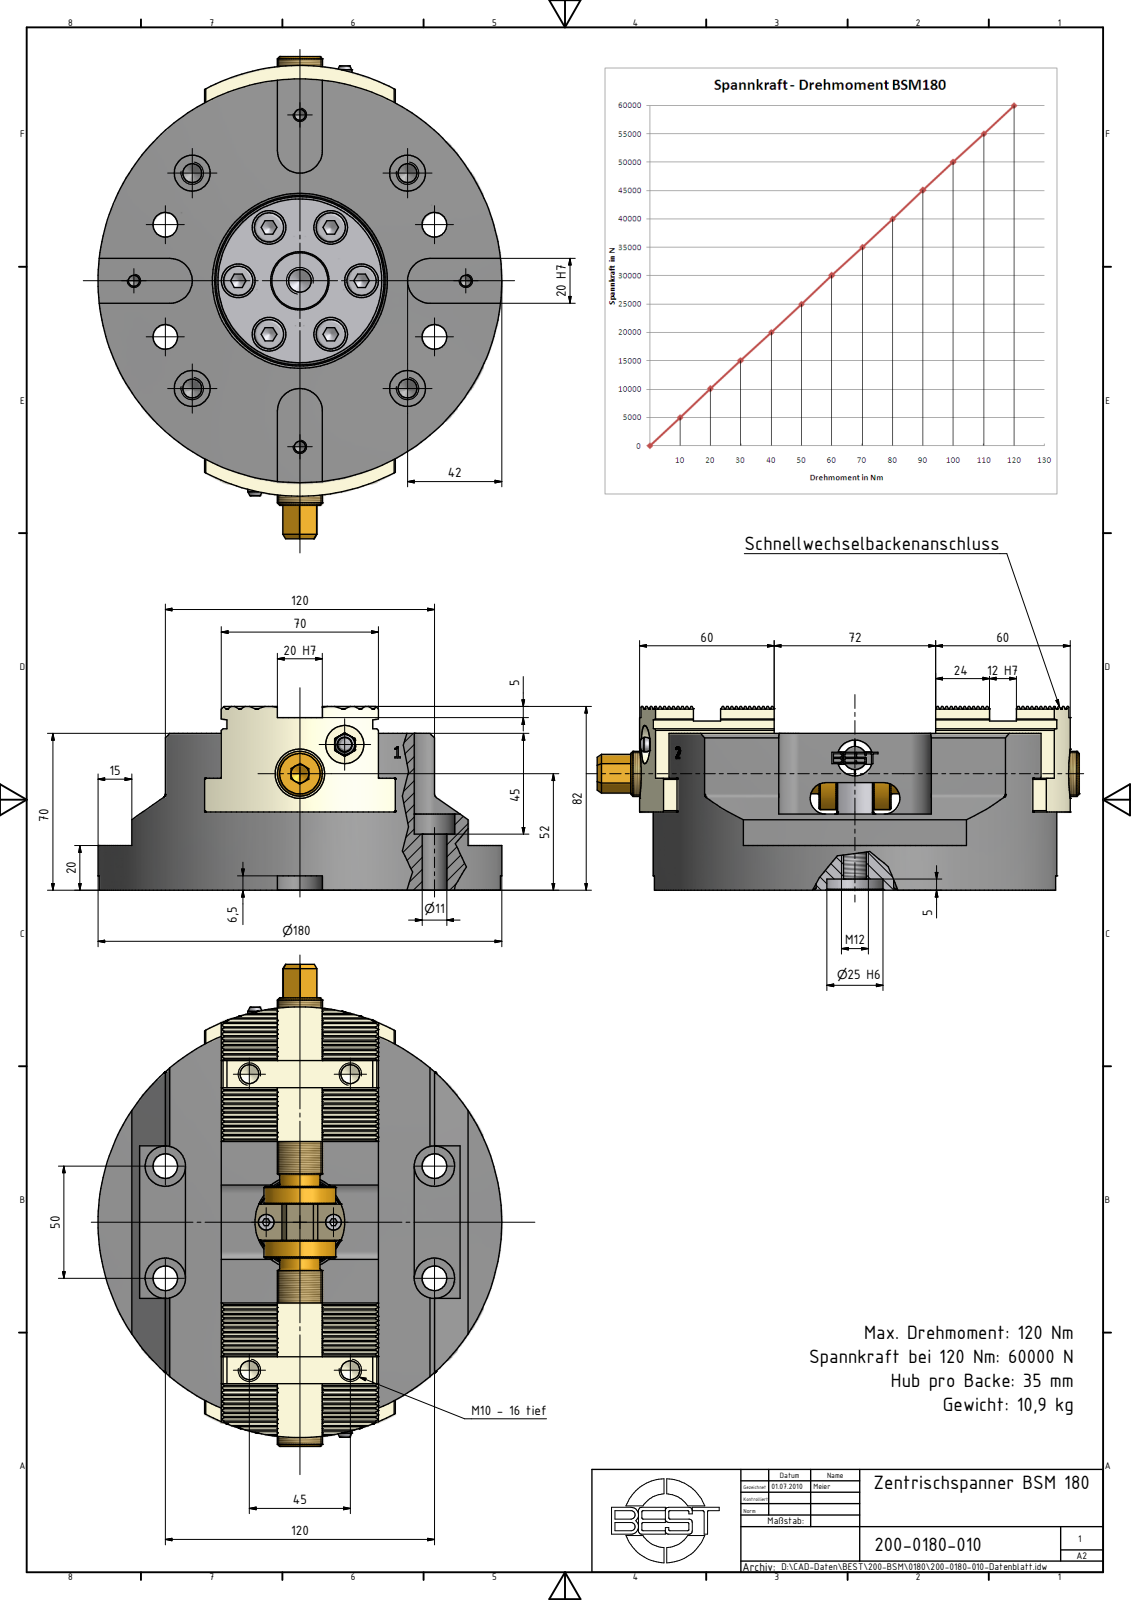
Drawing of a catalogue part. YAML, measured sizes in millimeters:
part_name: "200-0180-010-Kunde"
step_written_by: "Autodesk Inventor 2013 (AUTOMOTIVE_DESIGN)"
units: millimeters
bodies: {solids: 1, faces: 690, planar: 460, cylindrical: 137, other: 93}
overall_size: [215, 180, 97]
volume: 1424000
surface_area: 150710
round_holes:
  - {diameter: 8.38, count: 8}
  - {diameter: 4.92, count: 4}
  - {diameter: 11, count: 4}
  - {diameter: 16, count: 4}
  - {diameter: 18, count: 4}
  - {diameter: 6.92, count: 2}
  - {diameter: 17, count: 2}
  - {diameter: 10.11, count: 1}
  - {diameter: 25, count: 1}
  - {diameter: 40, count: 1}
  - {diameter: 76, count: 1}
round_bosses_or_shafts:
  - {diameter: 16, count: 4}
  - {diameter: 10, count: 4}
  - {diameter: 4, count: 2}
  - {diameter: 180, count: 1}
  - {diameter: 75, count: 1}
  - {diameter: 32, count: 1}
  - {diameter: 20, count: 1}
partial_cylinders:
  - {radius: 0.26, count: 18}
  - {radius: 0.64, count: 12}
  - {radius: 0.8, count: 4}
  - {radius: 1.44, count: 4}
  - {radius: 10, count: 4}
  - {radius: 2, count: 2}
  - {radius: 7, count: 2}
  - {radius: 90, count: 2}
face_to_face_distances: [70, 35, 15, 50, 20, 25, 82, 47, 12, 36]
hole_center_spacings: [54.59, 131.1, 23.88, 25.94, 28.65, 31.21, 55.56, 65]
